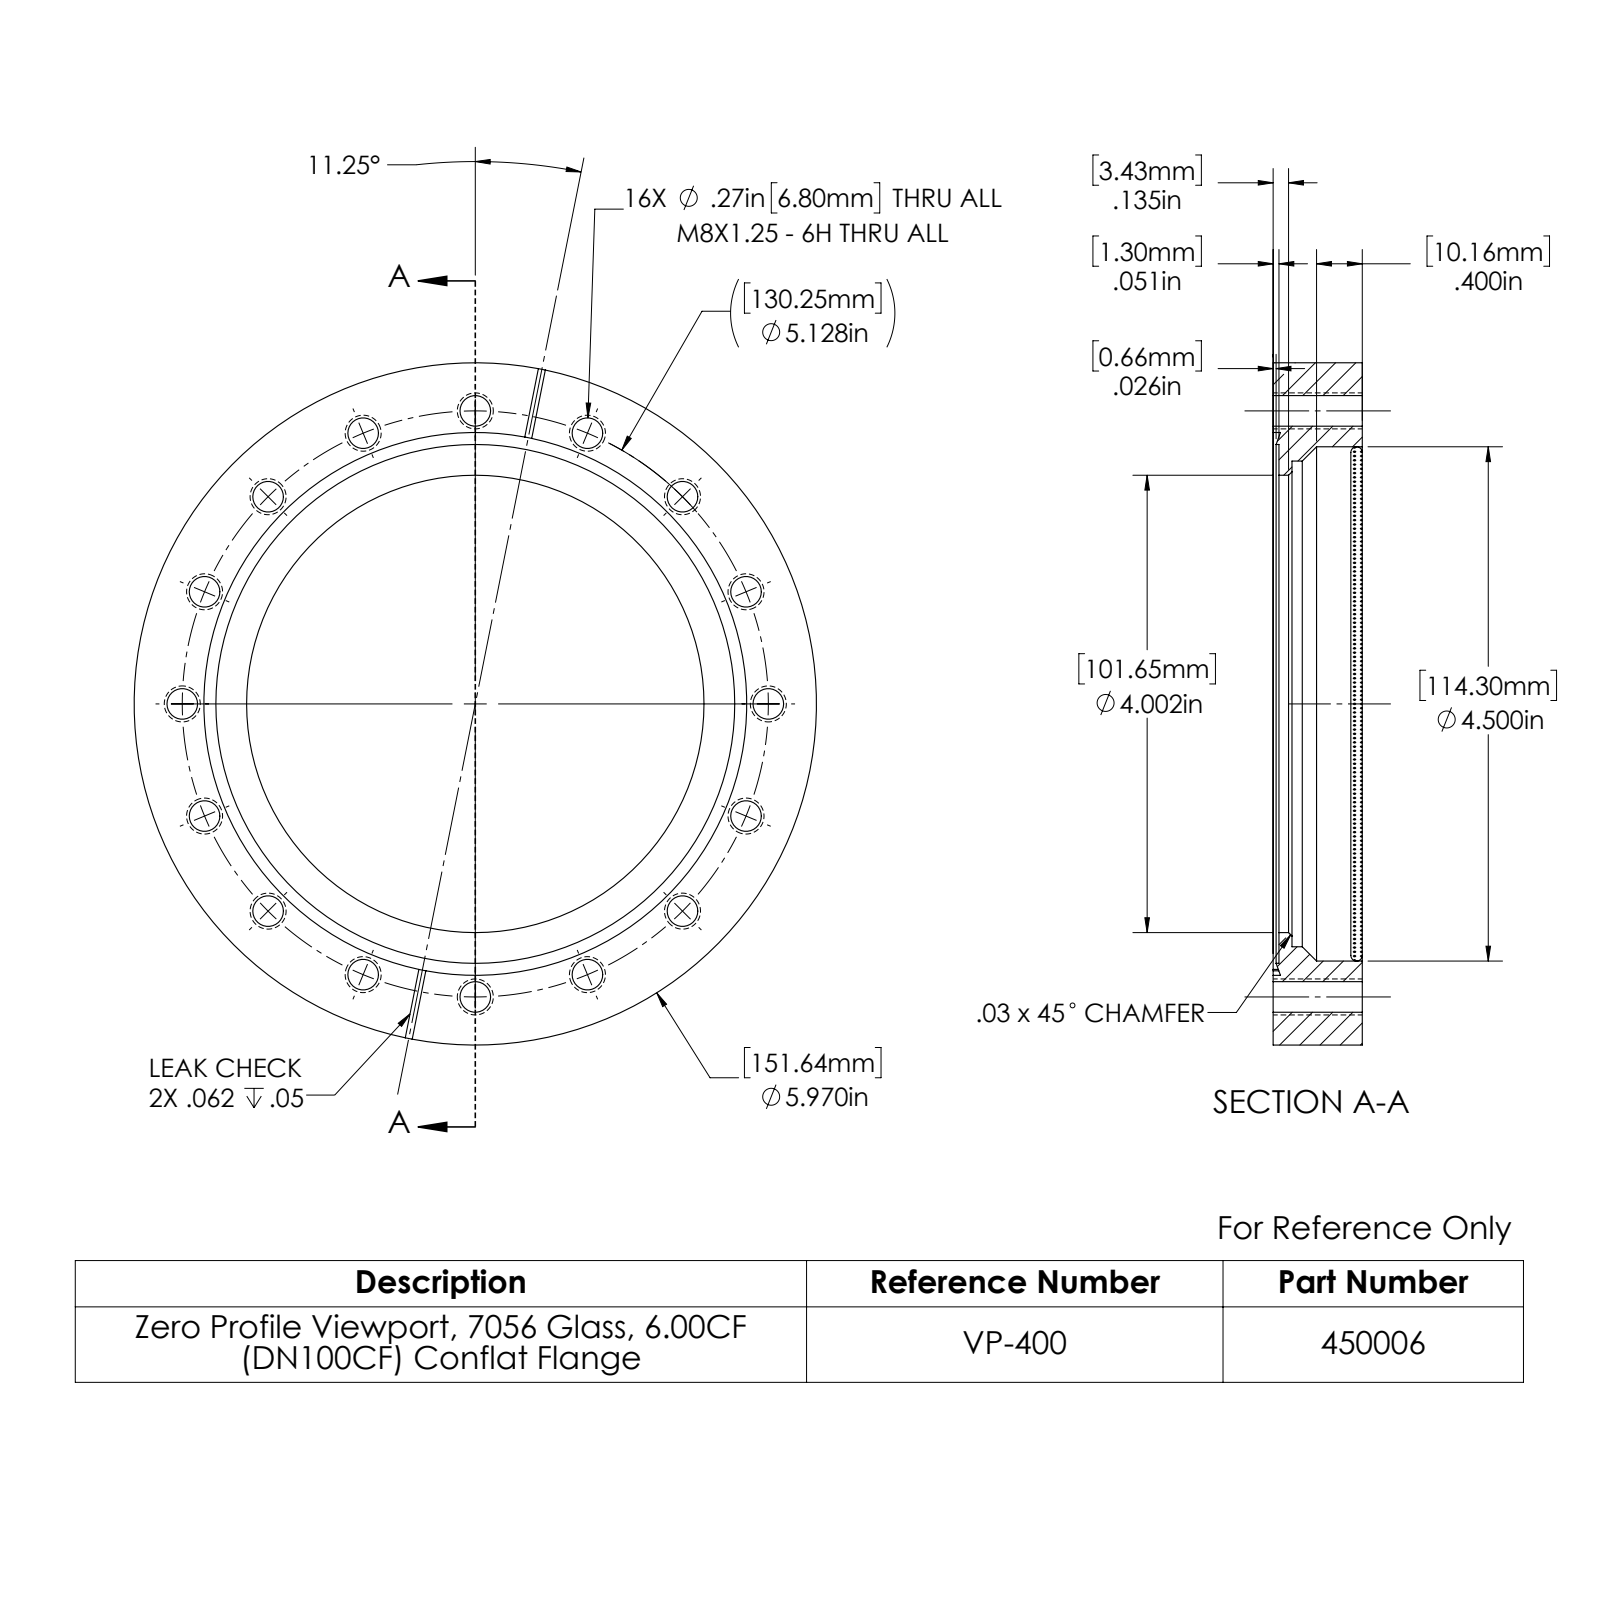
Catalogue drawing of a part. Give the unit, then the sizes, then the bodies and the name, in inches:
Units: inches
Overall size (bounding box): 5.97 × 5.97 × 0.78
Round holes (diameter × count): ⌀0.268 ×16, ⌀4.002 ×1, ⌀4.25 ×1, ⌀4.5 ×1, ⌀4.54 ×1, ⌀4.75 ×1
Round bosses / shafts (diameter × count): ⌀5.97 ×1
Main face-to-face distances: 0.1, 0.68, 0.78, 0.051, 0.629, 0.729, 0.165, 0.114, 0.515, 0.615
Hole centre spacings: 1, 4.264, 4.738, 5.03, 1.963, 2.564, 3.626, 2.849
Volume: 10.85 in³ · Surface area: 96.96 in²
Bodies: 2 solids, 60 faces (6 planar, 44 cylindrical, 10 other)
Part name (STEP PRODUCT): 450006
STEP written by: SolidWorks 2022 (AUTOMOTIVE_DESIGN)
